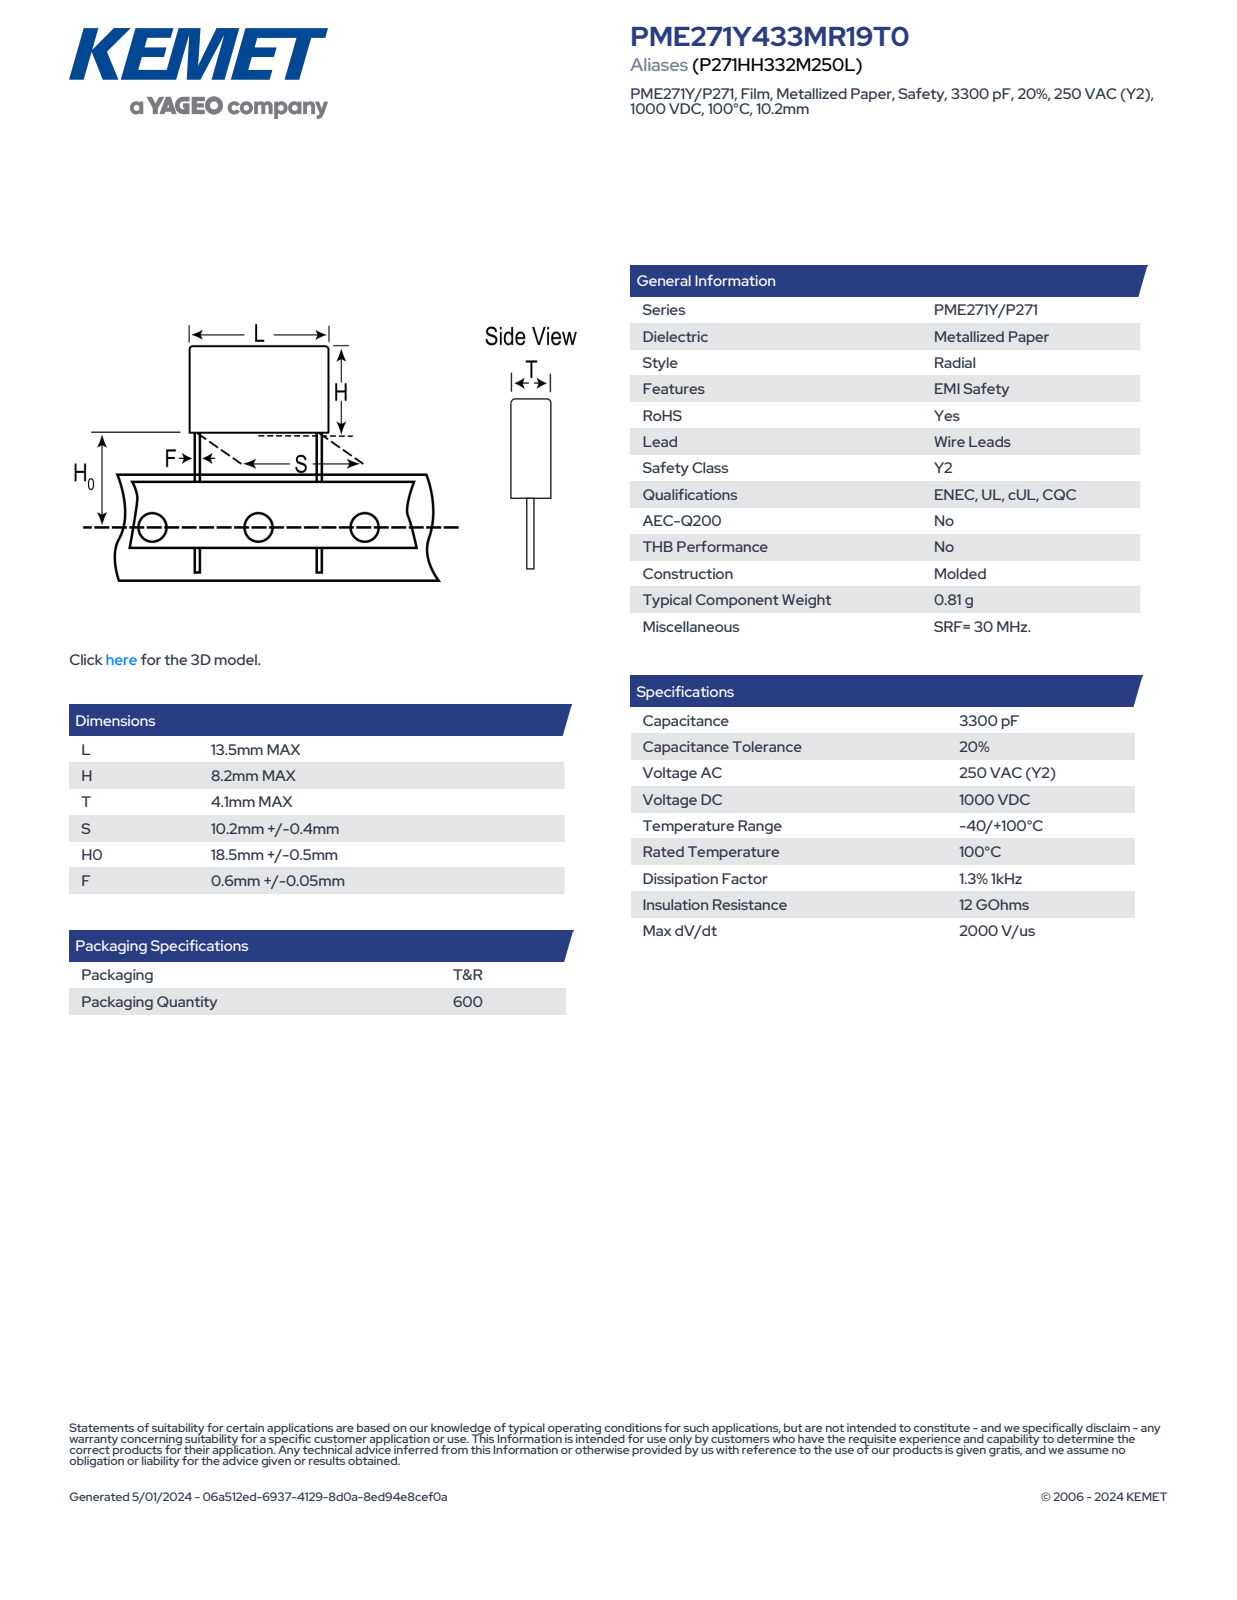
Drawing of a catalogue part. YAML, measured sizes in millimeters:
part_name: "CFR_MOLDED_13.5X8.2X4.1_L13.5H8.2T4.1S10.2H019F0.65"
step_written_by: "SolidWorks 2014 (AUTOMOTIVE_DESIGN)"
units: millimeters
bodies: {solids: 4, faces: 73, planar: 65, cylindrical: 8, other: 0}
overall_size: [27.2, 13.5, 4.11]
volume: 465
surface_area: 478
round_bosses_or_shafts:
  - {diameter: 0.65, count: 2}
partial_cylinders:
  - {radius: 0.5, count: 4}
face_to_face_distances: [4.1, 8.2, 13.5, 19, 27.2, 23.65, 4.65, 3.55, 22.44, 3.44]
